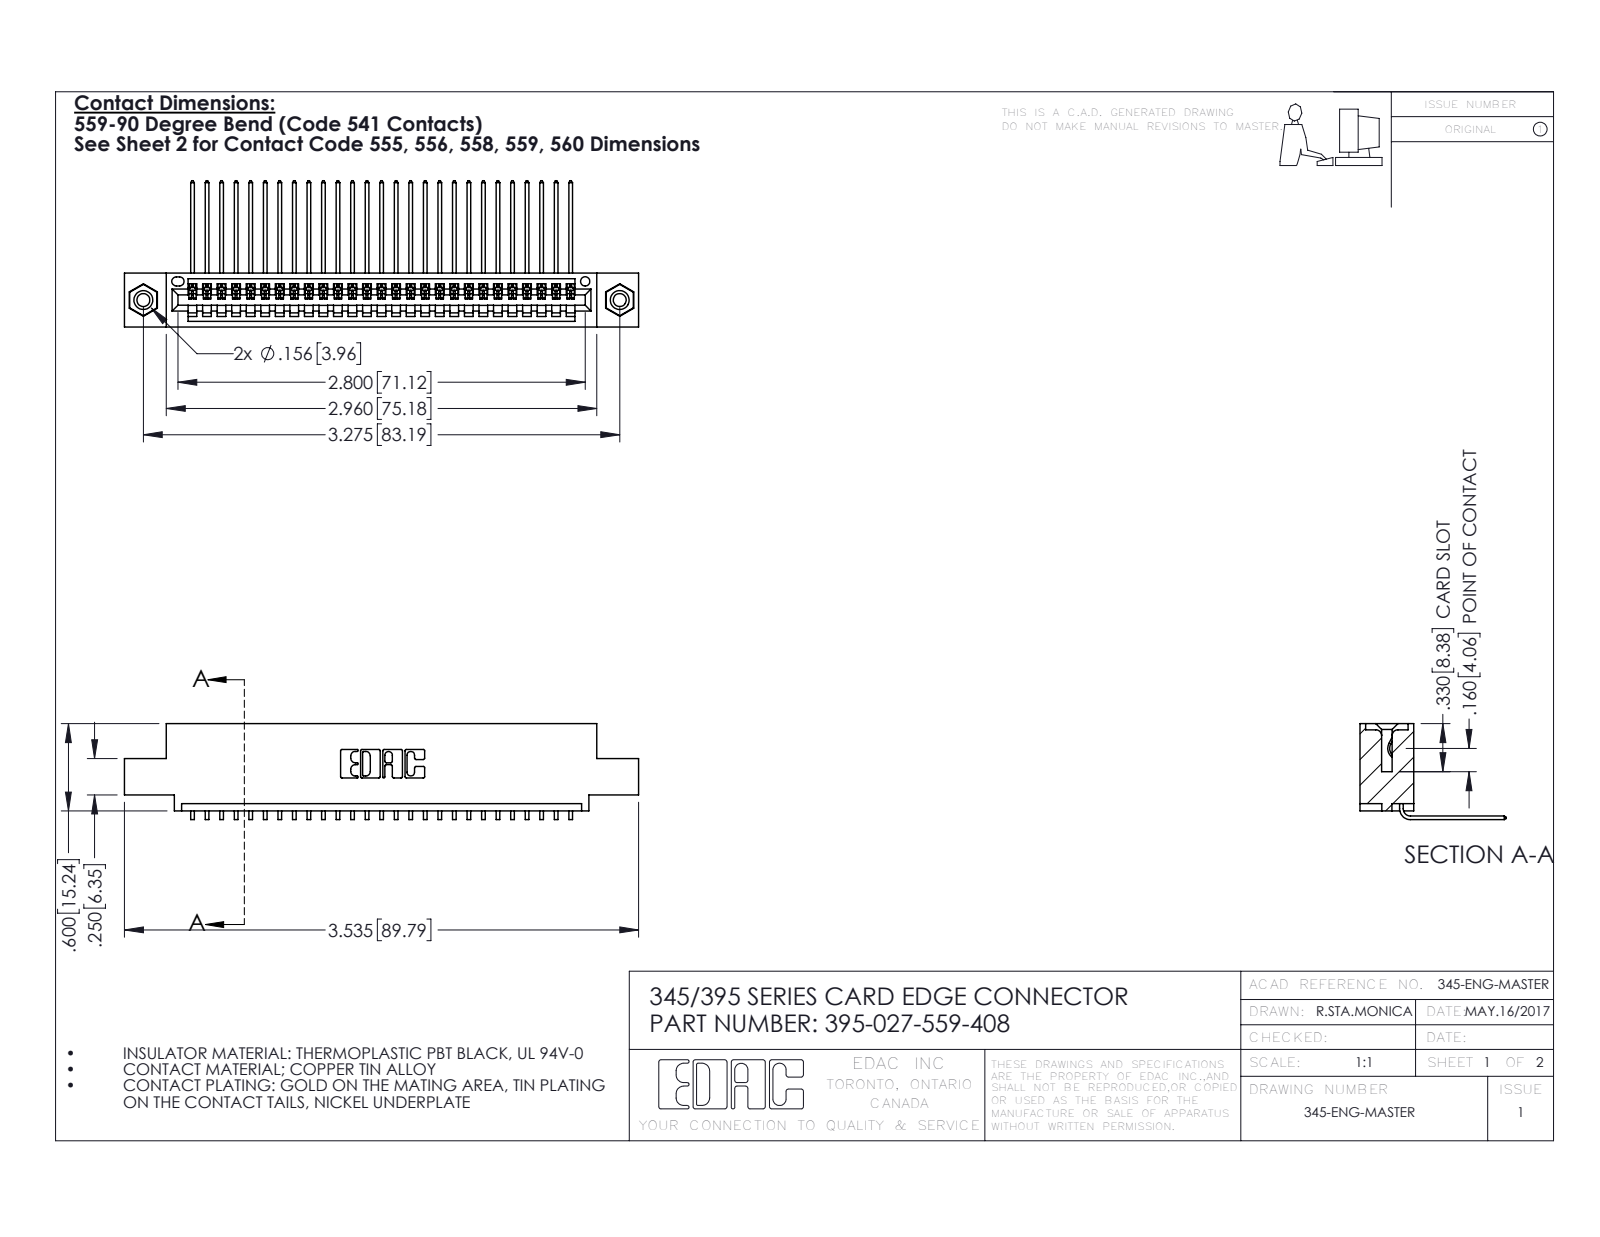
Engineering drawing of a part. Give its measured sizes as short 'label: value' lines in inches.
name: 395-027-559-408; 345-250-001_345-250-003-102; 345-292-001_558 559 Tail - 1; 345 Part_0.110 Offset - 0.156 Dia-TI
written by: SolidWorks 2016 (CONFIG_CONTROL_DESIGN)
unit: in
bodies: 30 solids, 1810 faces (1250 planar, 544 cylindrical, 16 other)
size: 3.535 × 1.005 × 0.659
volume: 0.514 in³; area: 17.99 in²
holes: 2× ⌀0.089, 2× ⌀0.125, 2× ⌀0.156, 1× ⌀0.064
bosses: 2× ⌀0.155
rounds: 54× R0.006, 22× R0.01, 6× R0.007, 6× R0.031, 3× R0.026, 2× R0.031, 2× R0.04, 1× R0.014
face distances: 0.072, 0.298, 0.37, 0.2, 0.098, 0.272, 0.025, 0.225, 0.149, 0.072
hole spacings: 0.27, 3.04, 3.275
